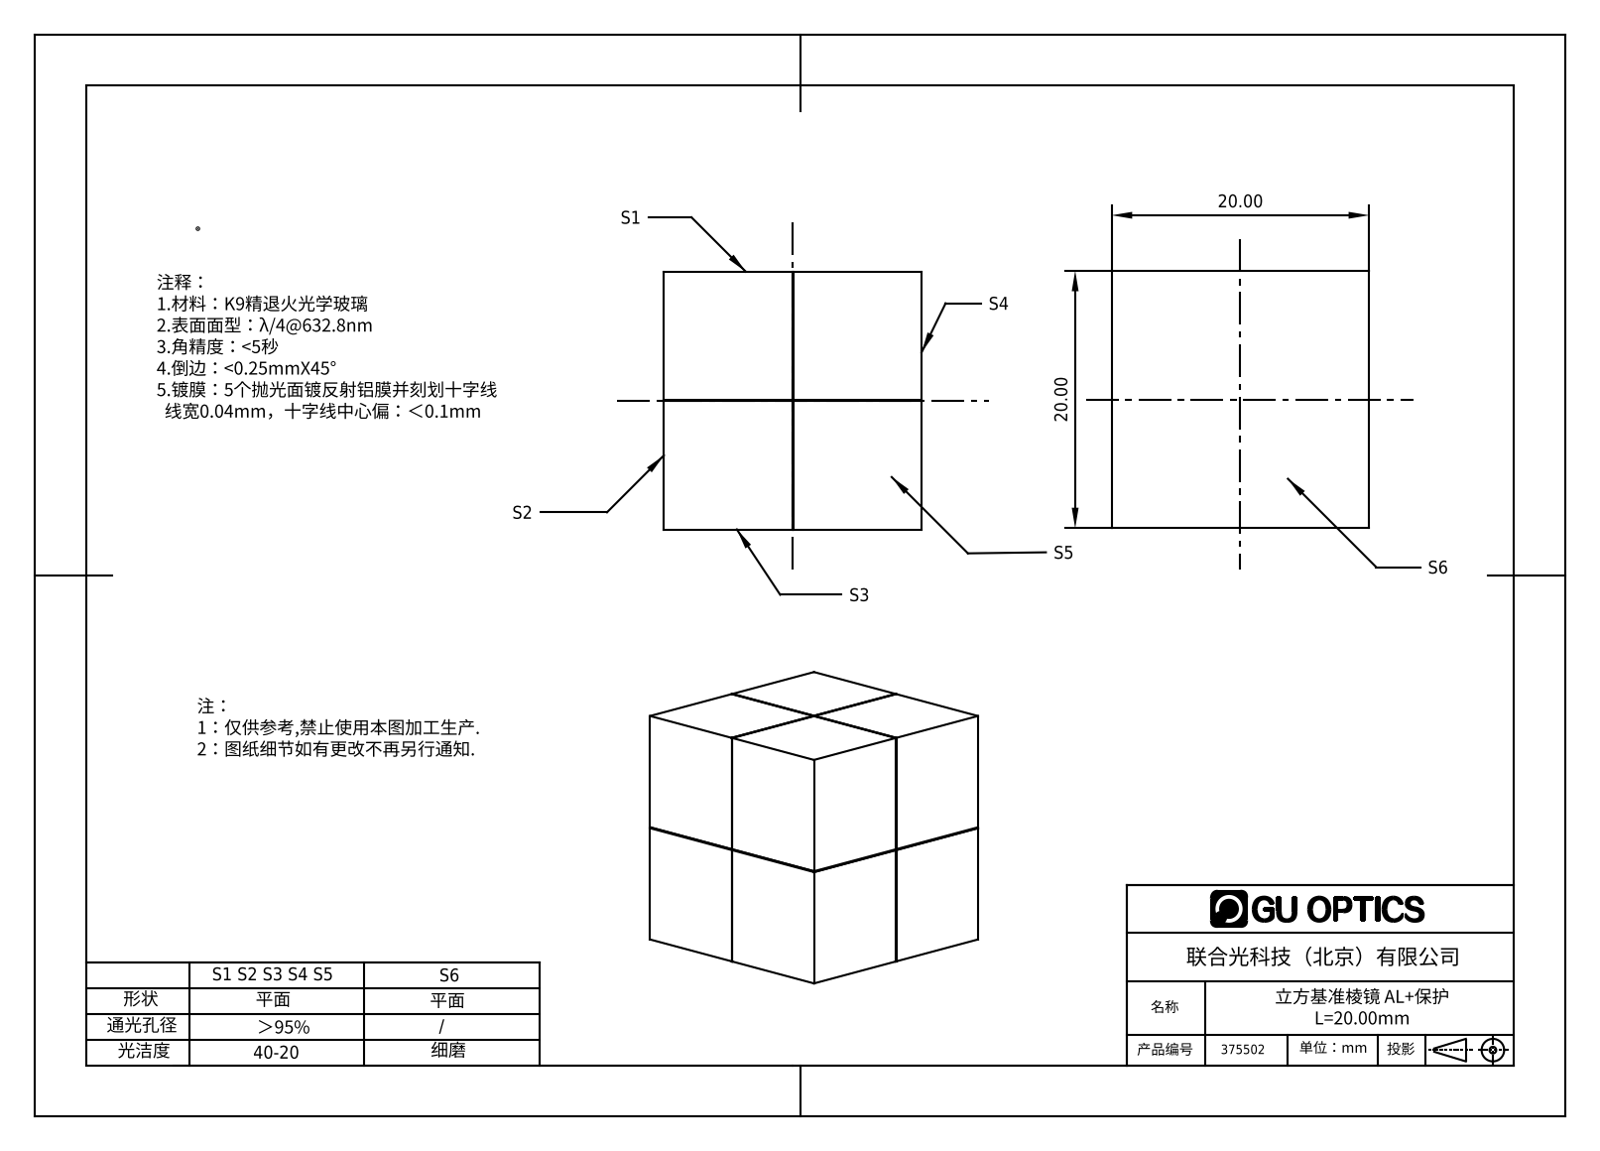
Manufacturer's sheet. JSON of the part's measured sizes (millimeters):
{"part_name": "374602", "step_written_by": "SolidWorks 2019 (CONFIG_CONTROL_DESIGN)", "units": "millimeters", "bodies": {"solids": 1, "faces": 66, "planar": 66, "cylindrical": 0, "other": 0}, "overall_size": [20, 20, 20], "volume_mm3": 8000, "surface_area_mm2": 2400, "face_to_face_distances": [20, 9.98, 10.02]}
